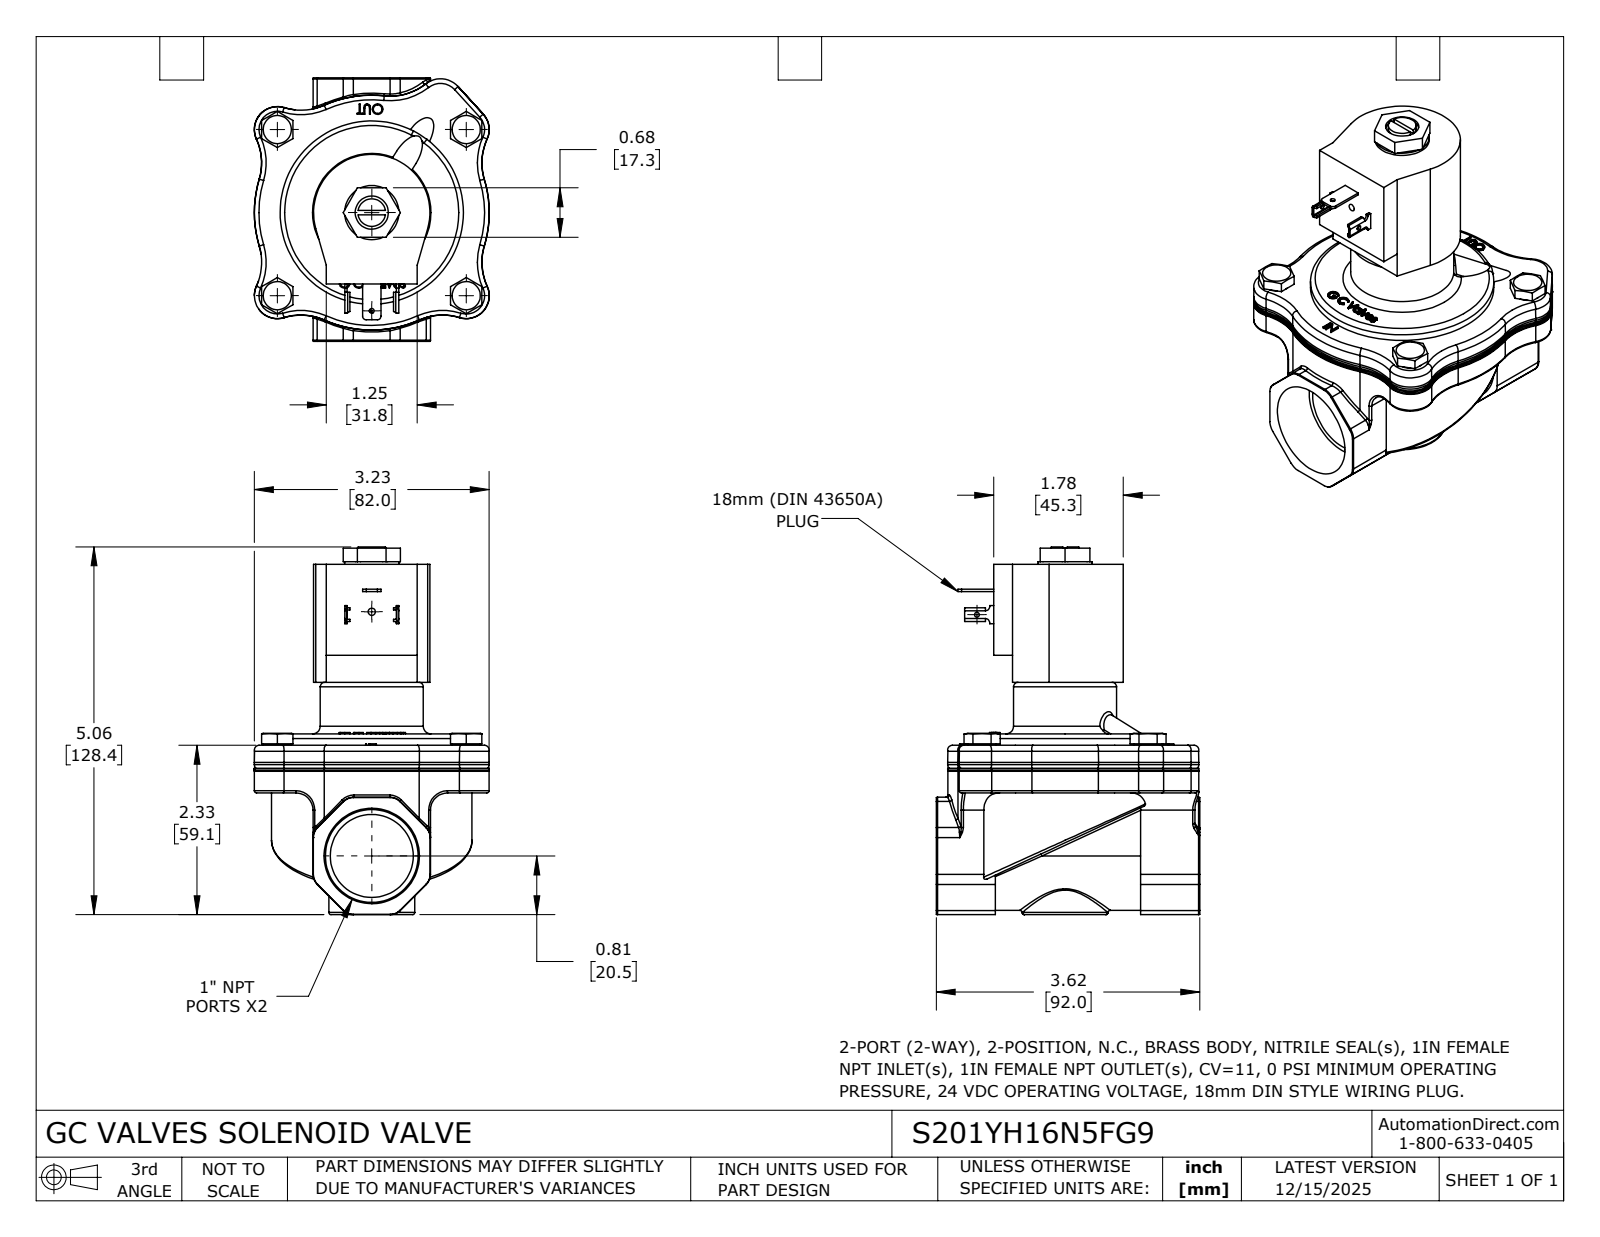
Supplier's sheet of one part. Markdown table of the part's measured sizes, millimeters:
| quantity | value |
| --- | --- |
| part name | S201YH16N5FG9 |
| STEP written by | SolidWorks 2024 (CONFIG_CONTROL_DESIGN) |
| units | millimeters |
| bodies | 1 solid, 671 faces (220 planar, 172 cylindrical, 279 other) |
| overall size | 128.4 × 92 × 82.1 |
| volume | 313 500 mm³ |
| surface area | 45 480 mm² |
| round holes (diameter × count) | 1.7 × 1, 1.7 × 1, 2.5 × 1, 11.6 × 1, 29 × 1 |
| round bosses / shafts (diameter × count) | 9.9 × 4, 64 × 1, 36 × 1, 30 × 1, 18.9 × 1, 9.7 × 1 |
| partial cylindrical surfaces (radius × count) | 0.8 × 24, 20 × 24, 8 × 12, 5 × 8, 0.2 × 4, 1 × 4, 1.3 × 2, 1.5 × 2 |
| main face-to-face distances | 4, 16.6, 20.6, 79.8, 63.1, 59.2, 63.1, 59.1, 42.5, 122.3 |
| hole center spacings | 34.3, 85.2 |
